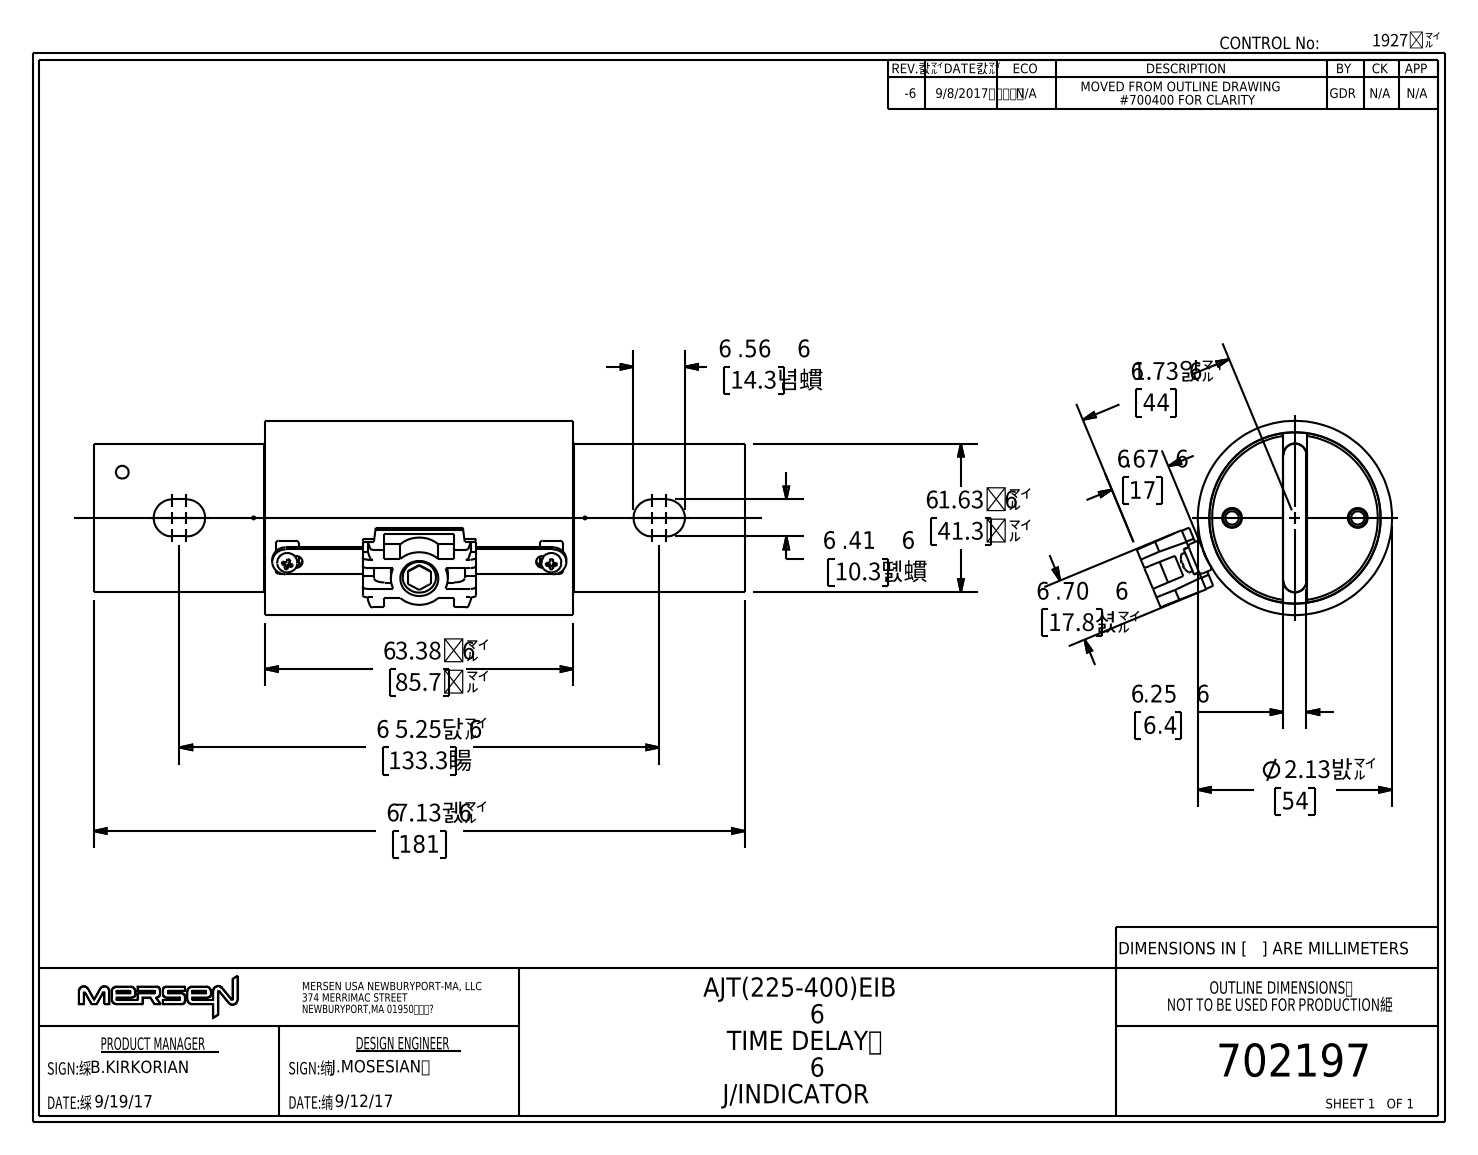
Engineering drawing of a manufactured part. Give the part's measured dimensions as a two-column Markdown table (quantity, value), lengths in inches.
| quantity | value |
| --- | --- |
| part name | 702197rev |
| STEP written by | SolidWorks 2016 (AUTOMOTIVE_DESIGN) |
| units | inches |
| bodies | 24 solids, 755 faces (374 planar, 246 cylindrical, 135 other) |
| overall size | 7.125 × 2.793 × 2.125 |
| volume | 6.74 in³ |
| surface area | 93.87 in² |
| round holes (diameter × count) | 0.17 × 3, 0.101 × 2, 0.125 × 2, 0.146 × 2, 0.187 × 2, 0.14 × 1, 1.875 × 1 |
| round bosses / shafts (diameter × count) | 0.219 × 2, 0.192 × 2, 0.112 × 2, 0.08 × 2, 2.125 × 1, 1.872 × 1, 0.365 × 1, 0.081 × 1 |
| partial cylindrical surfaces (radius × count) | 0.03 × 24, 0.005 × 14, 0.02 × 10, 0.06 × 10, 0.07 × 4, 0.203 × 4, 0.08 × 3, 0.115 × 2 |
| main face-to-face distances | 0.25, 0.438, 2.937, 3.375, 0.25, 0.25, 0.125, 2.499, 3.25, 0.313 |
| hole center spacings | 0.19, 0.687, 1.254, 1.444, 1.635, 0.38, 1.375, 2.889 |
